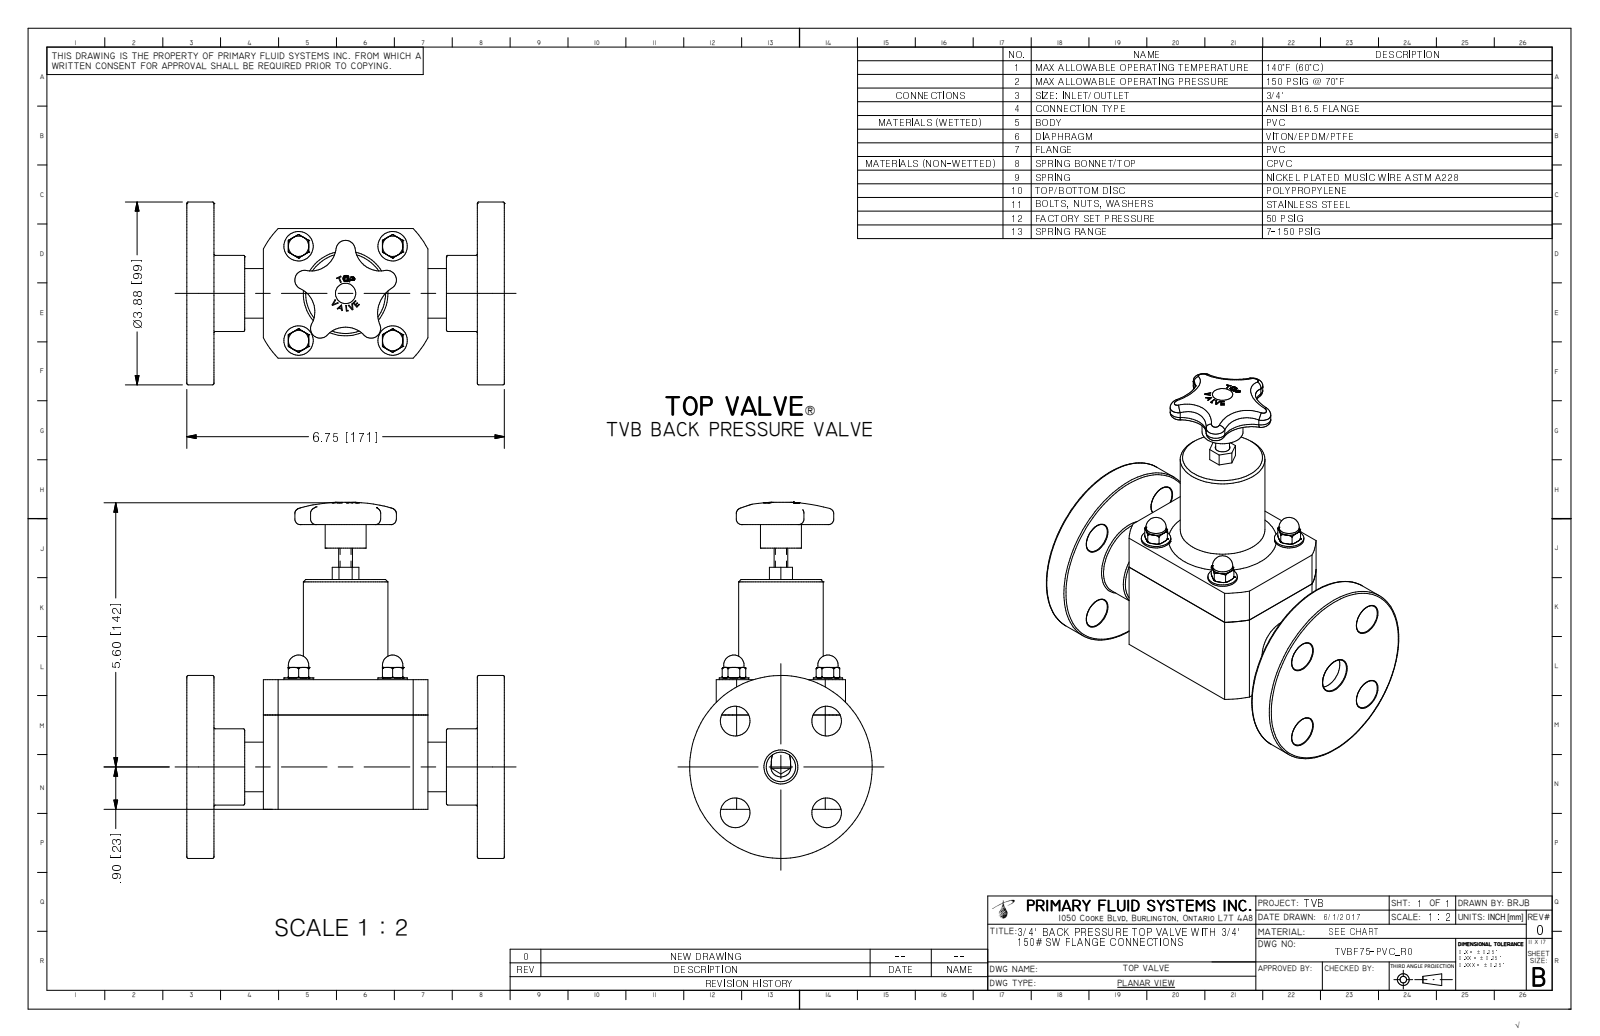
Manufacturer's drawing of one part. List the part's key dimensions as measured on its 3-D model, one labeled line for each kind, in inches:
Part name (STEP PRODUCT): TVBF75-PVC_R0
STEP written by: Autodesk Inventor 2009 (AUTOMOTIVE_DESIGN)
Units: inches
Bodies: 1 solid, 391 faces (152 planar, 61 cylindrical, 178 other)
Overall size (bounding box): 7.552 × 6.75 × 3.88
Volume: 46.37 in³ · Surface area: 167.9 in²
Round holes (diameter × count): ⌀0.175 ×4, ⌀0.63 ×4, ⌀0.722 ×1, ⌀0.742 ×1
Round bosses / shafts (diameter × count): ⌀0.625 ×4, ⌀0.433 ×4, ⌀0.375 ×4, ⌀3.88 ×1, ⌀1.8 ×1, ⌀1.616 ×1, ⌀1.05 ×1, ⌀0.87 ×1
Partial cylindrical surfaces — rounded edges, fillets, slot ends (radius × count): R0.085 ×5, R0.205 ×5, R0.536 ×4, R0.656 ×4, R0.625 ×1, R0.745 ×1, R1.988 ×1
Main face-to-face distances: 0.575, 6.175, 6.75, 1.625, 5.125, 1.05, 4.55, 5.6, 2.75, 3.5
Hole centre spacings: 1.375, 1.945, 2, 2.75, 2.828
